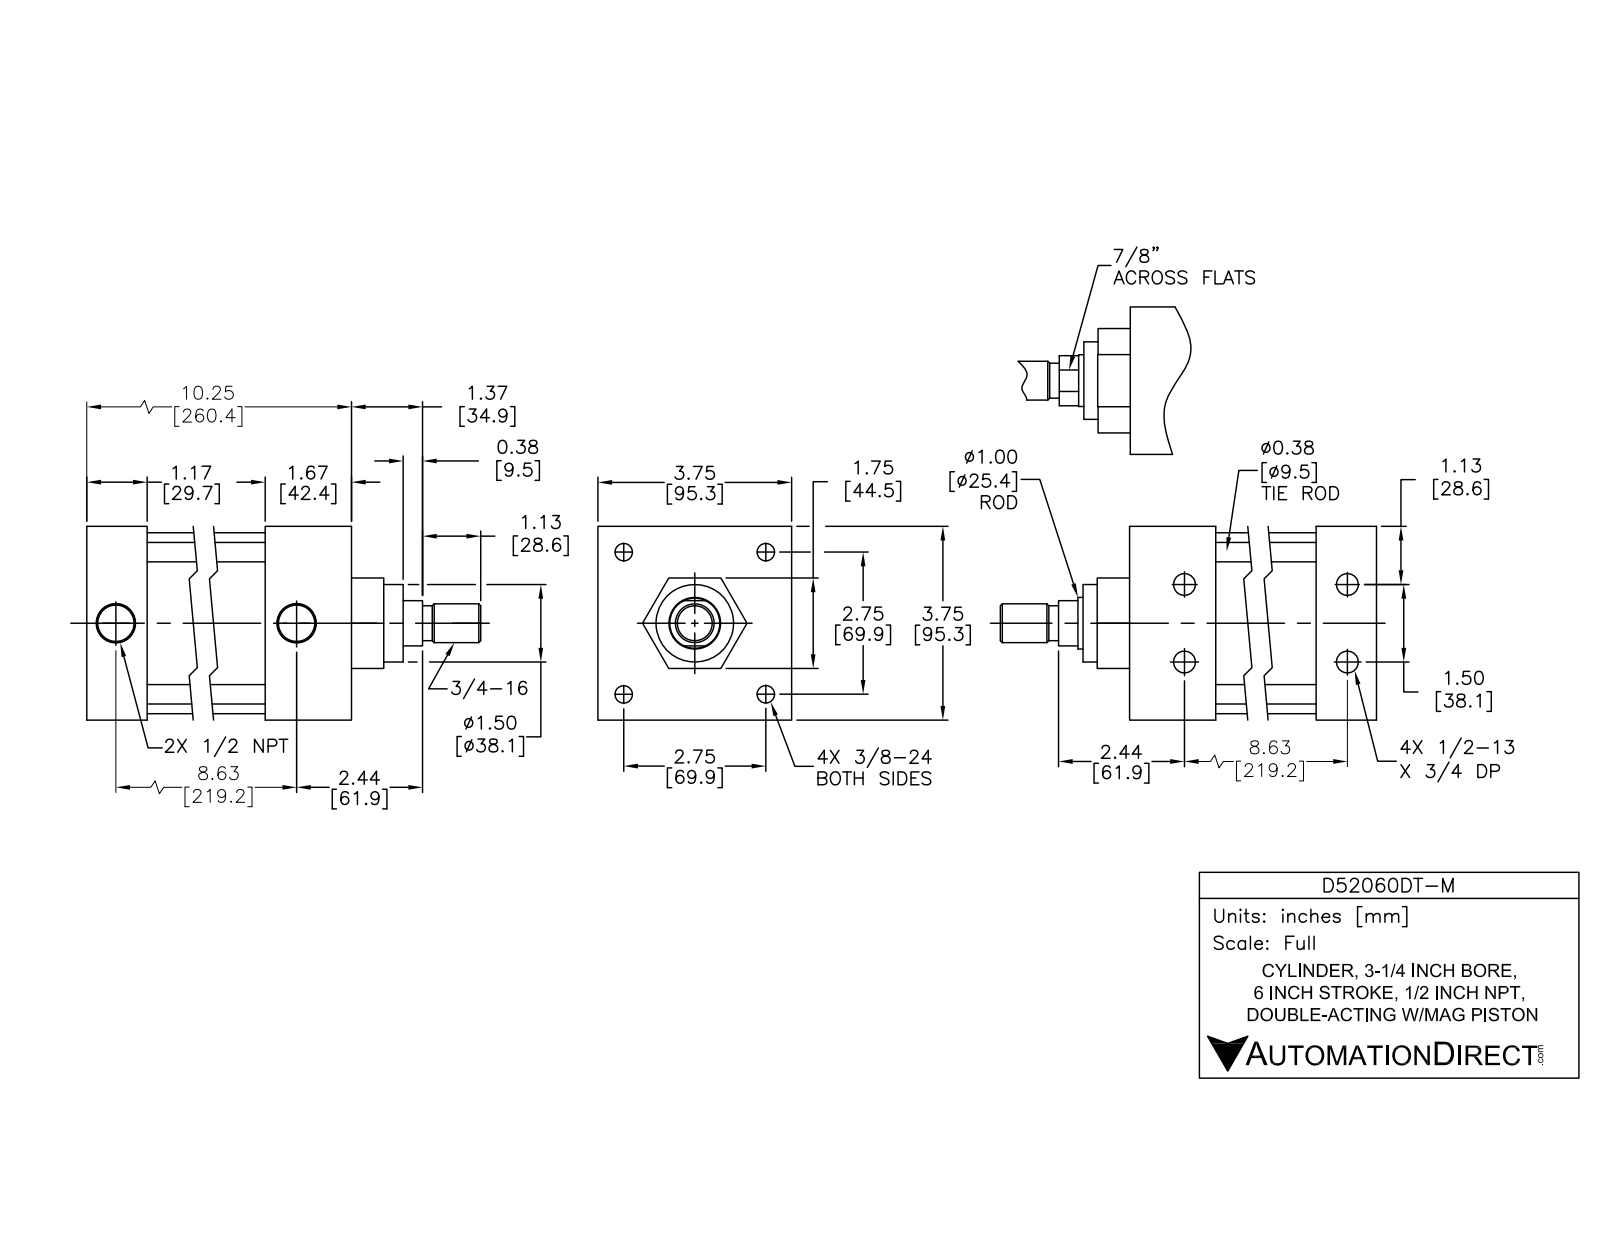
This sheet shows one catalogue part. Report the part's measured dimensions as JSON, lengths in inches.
{"part_name": "D52060DT-M; D52060DT-M PISTON; D52060DT-M BODY", "step_written_by": "SolidWorks 2015 (AUTOMOTIVE_DESIGN)", "units": "inches", "bodies": {"solids": 12, "faces": 303, "planar": 99, "cylindrical": 114, "other": 90}, "overall_size": [12.745, 3.75, 3.75], "volume_in3": 68.64, "surface_area_in2": 408.7, "round_holes": [[0.33, 4], [0.406, 4], [0.417, 4], [0.625, 4], [0.5, 2], [0.766, 2], [1, 1], [1.003, 1], [3.25, 1]], "round_bosses_or_shafts": [[0.609, 4], [0.375, 4], [0.34, 4], [3.5, 1], [3.247, 1], [1.75, 1], [0.997, 1], [0.97, 1]], "partial_cylinders_radius": [[0.375, 4]], "face_to_face_distances": [3.75, 0.08, 7.326, 10.246, 1.75, 8.997, 1.249, 7.751, 1.246, 2.495], "hole_center_spacings": [2.758, 1.95, 0.75, 0.76, 1.5, 3.9, 8.5, 8.537]}
